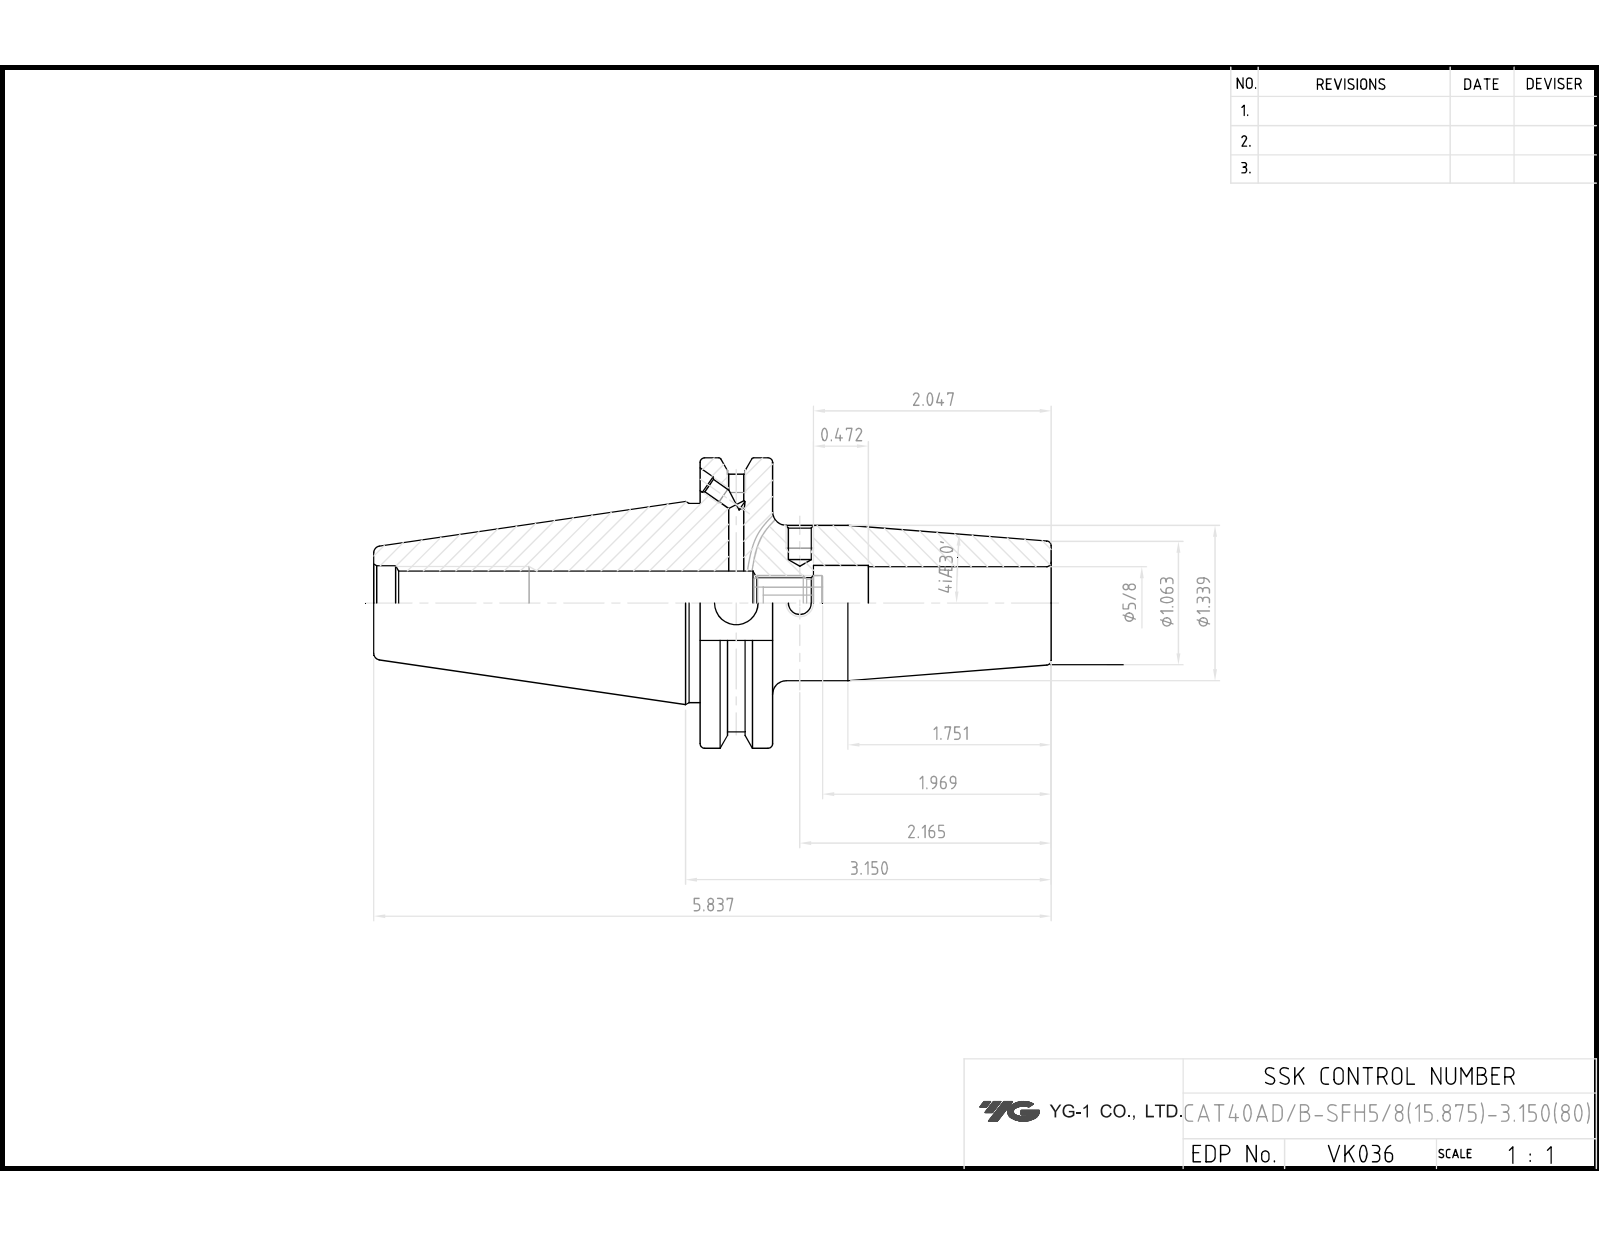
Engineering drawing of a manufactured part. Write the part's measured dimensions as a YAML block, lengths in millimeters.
part_name: "LO-CAT40ADB-SFH15.875-80"
step_written_by: "Autodesk Inventor 2020 (AUTOMOTIVE_DESIGN)"
units: millimeters
bodies: {solids: 1, faces: 87, planar: 37, cylindrical: 29, other: 21}
overall_size: [148.25, 63.5, 61.09]
volume: 137409
surface_area: 29162
round_holes:
  - {diameter: 3.24, count: 4}
  - {diameter: 4, count: 2}
  - {diameter: 4.2, count: 2}
  - {diameter: 9.53, count: 1}
  - {diameter: 10.92, count: 1}
  - {diameter: 13, count: 1}
  - {diameter: 13.39, count: 1}
  - {diameter: 15.88, count: 1}
  - {diameter: 16.3, count: 1}
  - {diameter: 16.47, count: 1}
round_bosses_or_shafts:
  - {diameter: 63.5, count: 1}
  - {diameter: 43.6, count: 1}
  - {diameter: 34, count: 1}
partial_cylinders:
  - {radius: 28.15, count: 1}
face_to_face_distances: [15.88, 76.83, 60.95, 47.6, 16.38, 71.42, 87.3, 148.25, 96.25, 24.83]
